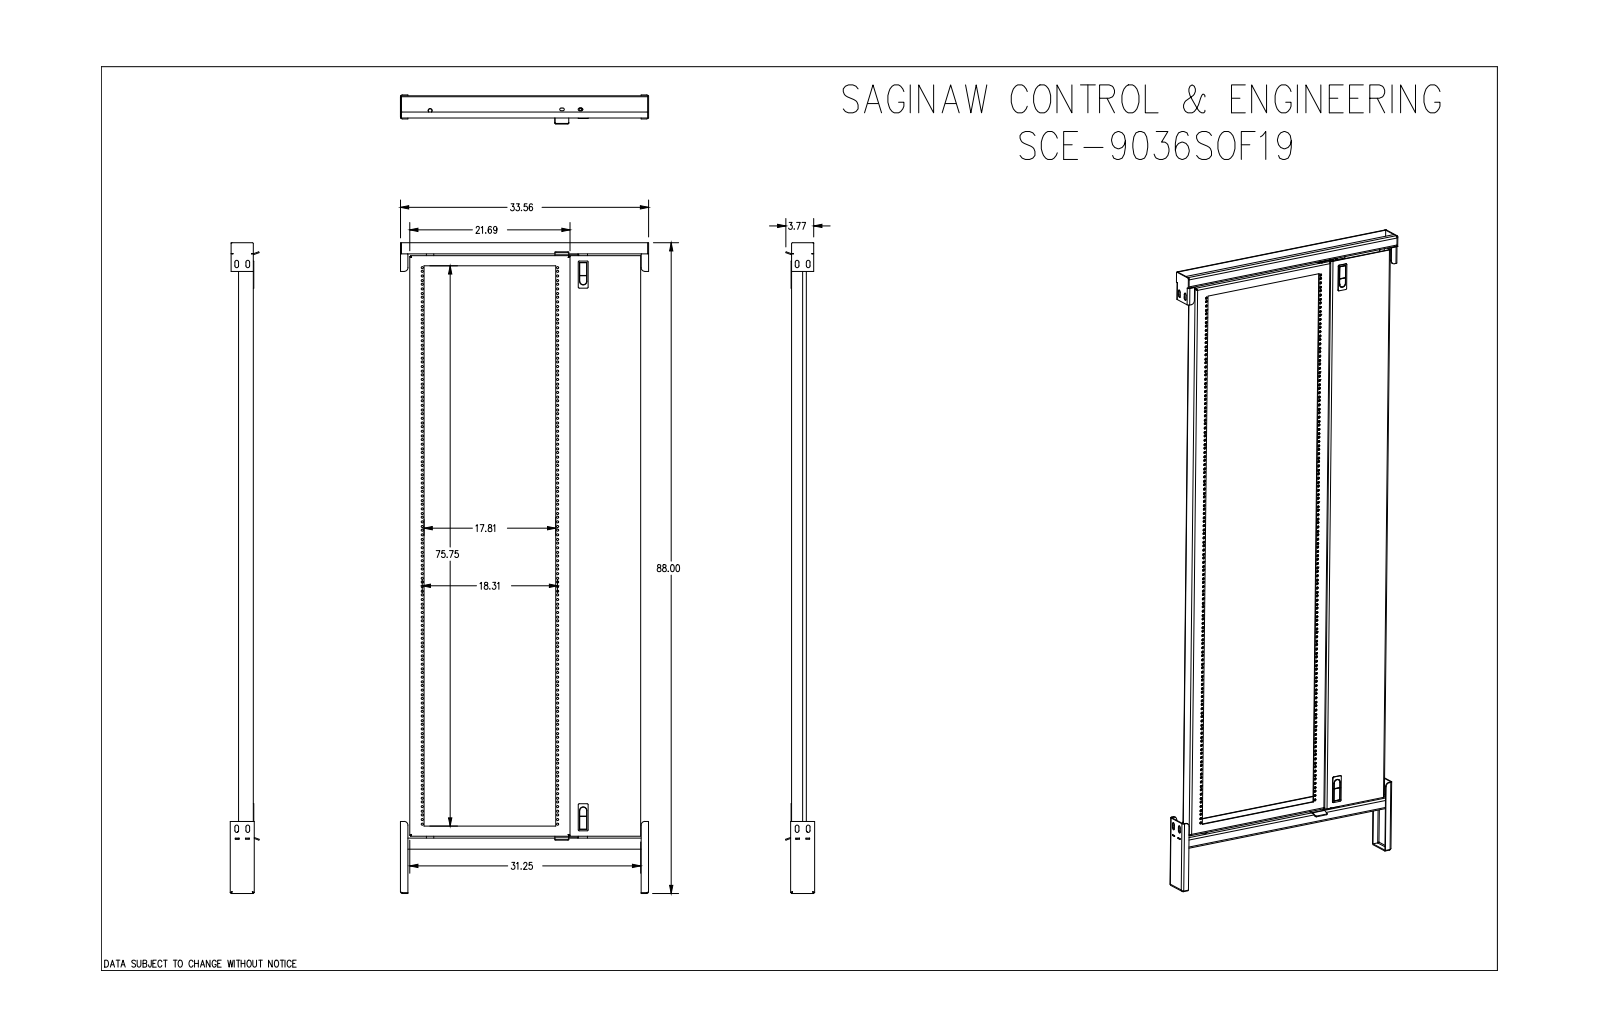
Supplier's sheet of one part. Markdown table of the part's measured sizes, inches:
| quantity | value |
| --- | --- |
| part name | SCE-9036SOF19 |
| STEP written by | SolidWorks 2019 (AUTOMOTIVE_DESIGN) |
| units | inches |
| bodies | 38 solids, 1525 faces (517 planar, 935 cylindrical, 73 other) |
| overall size | 87.996 × 33.568 × 3.922 |
| volume | 294 in³ |
| surface area | 4 812 in² |
| round holes (diameter × count) | 0.281 × 260, 0.17 × 11, 0.193 × 11, 0.218 × 11, 0.375 × 2, 0.375 × 2, 0.531 × 2, 0.5 × 1, 0.503 × 1 |
| round bosses / shafts (diameter × count) | 0.26 × 11, 0.19 × 11, 0.16 × 2, 1 × 1 |
| partial cylindrical surfaces (radius × count) | 0.025 × 99, 0.021 × 77, 0.125 × 62, 0.01 × 46, 0.25 × 46, 0.059 × 22, 0.087 × 22, 0.031 × 12 |
| main face-to-face distances | 0.125, 0.125, 21.563, 1.875, 9.435, 2.875, 1, 0.25, 79.118, 1.75 |
| hole center spacings | 1.75, 3.5, 5.25, 7, 8.75, 10.5, 7.625, 7.625 |
